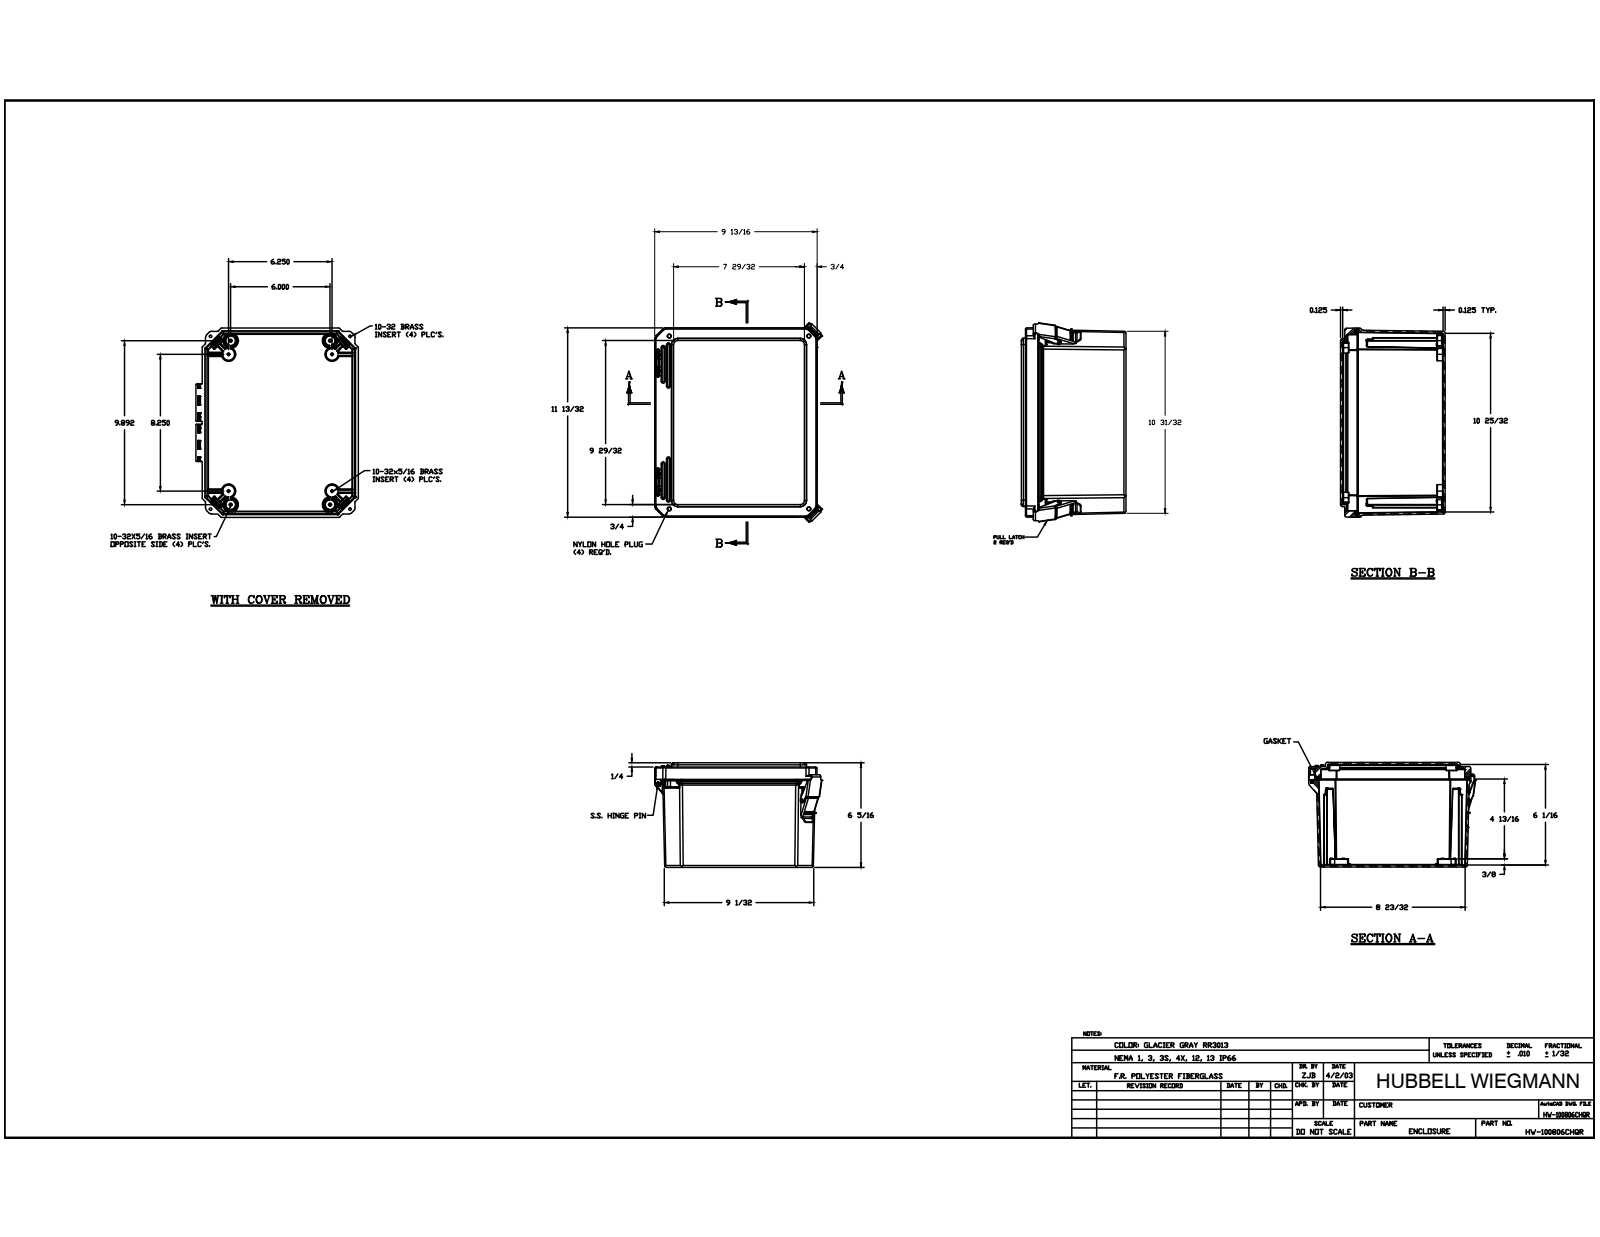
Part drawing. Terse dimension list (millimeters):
name: DS100806BOX; BRASS INSERT-(; BRASS INSERT-(_1; BRASS INSERT-(_2 (+6 more)
written by: Autodesk Inventor 2014 (AUTOMOTIVE_DESIGN)
unit: mm
bodies: 35 solids, 2433 faces (813 planar, 988 cylindrical, 632 other)
size: 307.65 × 257.72 × 160.28
volume: 1 168 000 mm³; area: 655 189 mm²
holes: 16× ⌀3.96, 11× ⌀3.43, 8× ⌀3.86, 4× ⌀3.81, 4× ⌀6.4, 4× ⌀6.43, 2× ⌀3.43, 2× ⌀5.56, 2× ⌀5.77, 2× ⌀7.94, 2× ⌀9.52, 1× ⌀3.48
bosses: 16× ⌀6.25, 4× ⌀22.1, 4× ⌀7.62, 4× ⌀5.3, 2× ⌀11.05, 1× ⌀3.43
rounds: 203× R0.25, 84× R0.51, 80× R0.13, 65× R0.76, 35× R1.52, 26× R1.59, 26× R2.29, 24× R0.76
face distances: 3.17, 157.11, 3.23, 3.2, 160.28, 153.94, 6.35, 150.76, 3.18, 153.93
hole spacings: 6.35, 238.74, 301.59, 316.4, 39, 156.97, 188.37, 21.09
